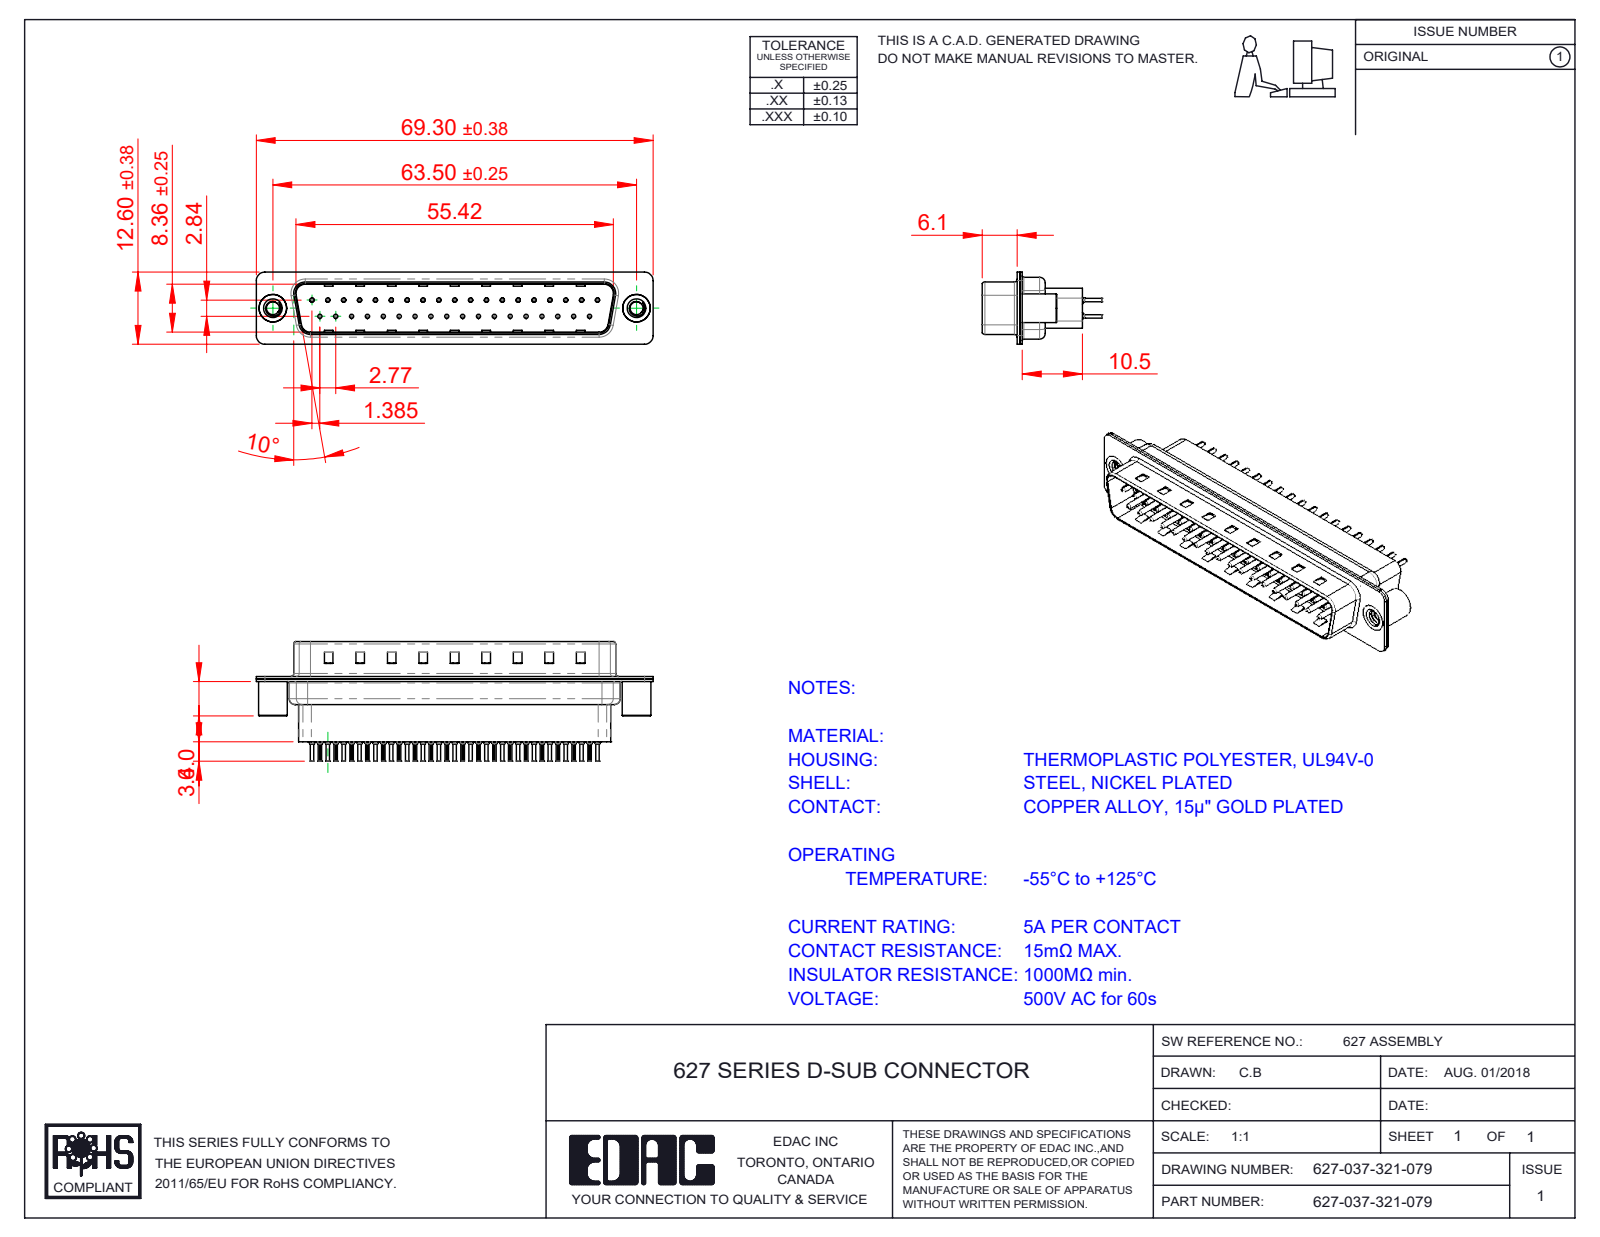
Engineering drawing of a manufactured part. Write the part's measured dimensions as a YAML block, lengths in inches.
part_name: "627 4-40 Threaded Standoff BS; 627 Housing_37 HP; 627 Shell Front_37 Contacts; 627-037-321-079 (+3 more)"
step_written_by: "SolidWorks 2020 (CONFIG_CONTROL_DESIGN)"
units: inches
bodies: {solids: 42, faces: 4060, planar: 1091, cylindrical: 1530, other: 1439}
overall_size: [2.728, 0.819, 0.496]
volume: 0.33
surface_area: 21.31
round_holes:
  - {diameter: 0.008, count: 37}
  - {diameter: 0.014, count: 37}
  - {diameter: 0.043, count: 37}
  - {diameter: 0.063, count: 37}
  - {diameter: 0.089, count: 2}
  - {diameter: 0.157, count: 2}
  - {diameter: 0.189, count: 2}
round_bosses_or_shafts:
  - {diameter: 0.079, count: 37}
  - {diameter: 0.059, count: 37}
  - {diameter: 0.03, count: 37}
  - {diameter: 0.024, count: 37}
  - {diameter: 0.197, count: 2}
  - {diameter: 0.193, count: 2}
partial_cylinders:
  - {radius: 0.004, count: 74}
  - {radius: 0.059, count: 16}
  - {radius: 0.079, count: 12}
  - {radius: 0.02, count: 8}
  - {radius: 0.063, count: 8}
  - {radius: 0.01, count: 4}
  - {radius: 0.024, count: 4}
  - {radius: 0.026, count: 4}
face_to_face_distances: [0.016, 0.032, 0.377, 0.027, 0.302, 0.018, 0.059, 0.043, 0.318, 0.345]
hole_center_spacings: [0.124, 0.109, 0.218, 0.327, 0.198, 0.398, 0.436, 0.503]
